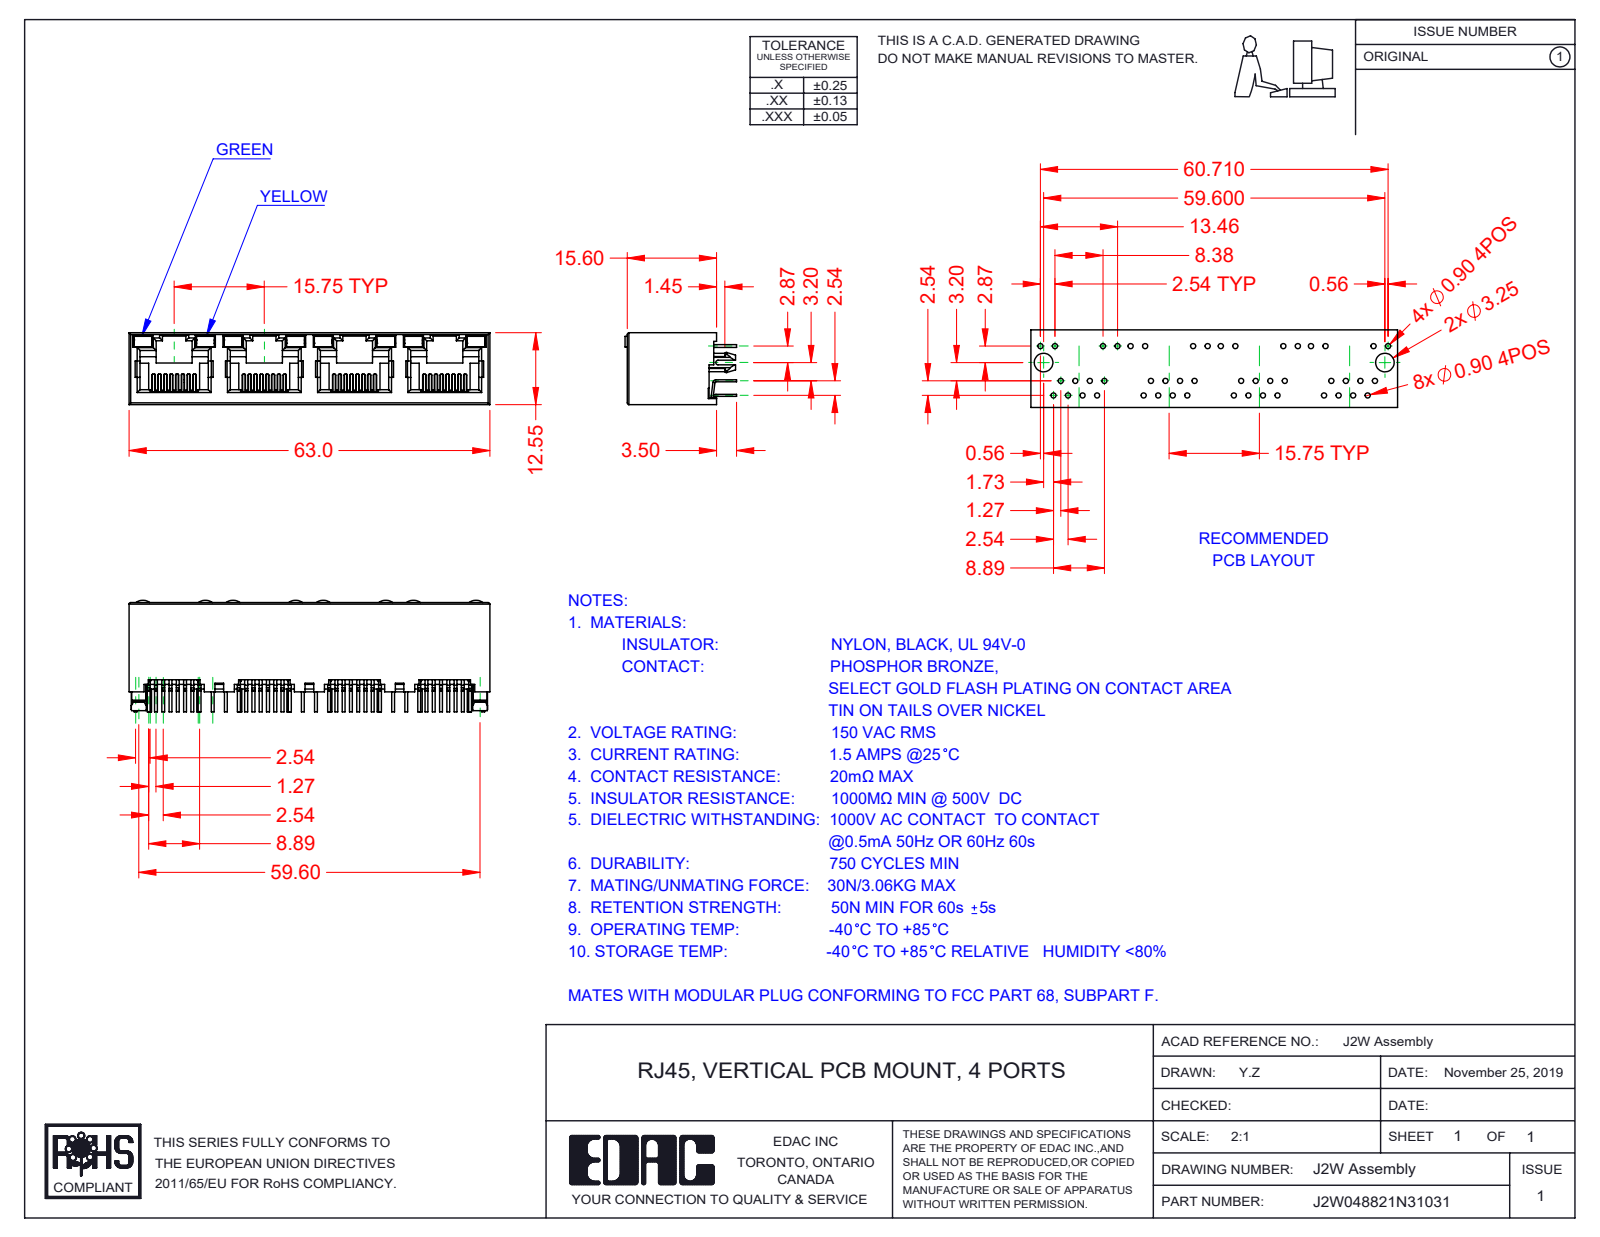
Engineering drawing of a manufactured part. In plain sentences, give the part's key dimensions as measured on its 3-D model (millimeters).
The part is named "2W Contact Lock; J2W048821N31131; 2W LED LH_3-Green; 2W Insulator (+2 more)". Its 3-D file was written by "SolidWorks 2016 (CONFIG_CONTROL_DESIGN)". It is 45 solids with 3135 faces: 2600 planar, 477 cylindrical and 58 other. Overall it measures 63 by 19.5 by 12.55 millimeters. Its volume is 5 335 cubic millimeters and its surface area 13 144 square millimeters. Partial cylindrical surfaces (rounded edges, fillets, slot ends): 64 of radius 0.15, 29 of radius 0.2, 28 of radius 0.5, 14 of radius 0.3, 8 of radius 0.45, 8 of radius 2, 2 of radius 0.25, 2 of radius 1.5. The main face-to-face distances are 12.55, 11.9, 0.65, 15.75, 0.36, 1.5, 0.78, 0.6, 11.3, 31.5.
